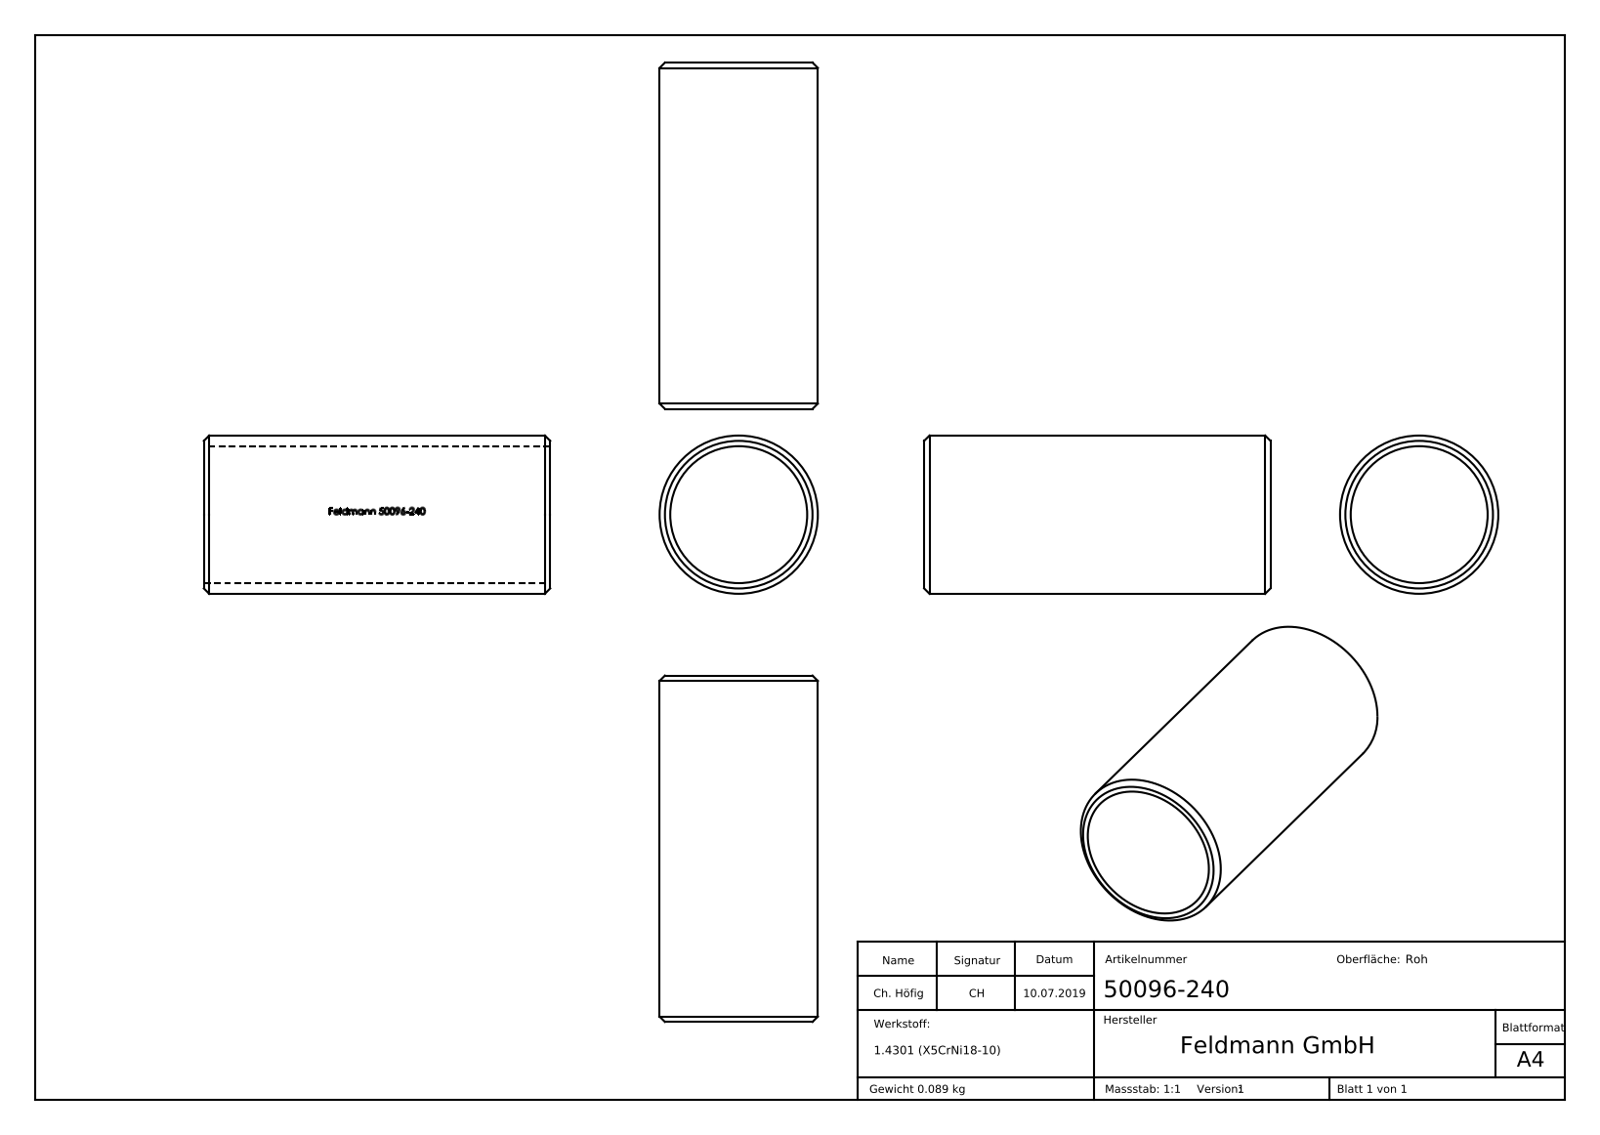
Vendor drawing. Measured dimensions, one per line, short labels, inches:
name: 50096-240
written by: SolidWorks 2015 (CONFIG_CONTROL_DESIGN)
unit: in
bodies: 1 solid, 247 faces (91 planar, 45 cylindrical, 111 other)
size: 2.559 × 1.169 × 1.169
volume: 0.685 in³; area: 17.92 in²
holes: 1× ⌀1.012
bosses: 1× ⌀1.169
rounds: 1× R0.51
face distances: 2.559, 0.015, 0.117, 0.052, 0.576, 0.044, 0.161, 0.017, 0.05, 0.035
